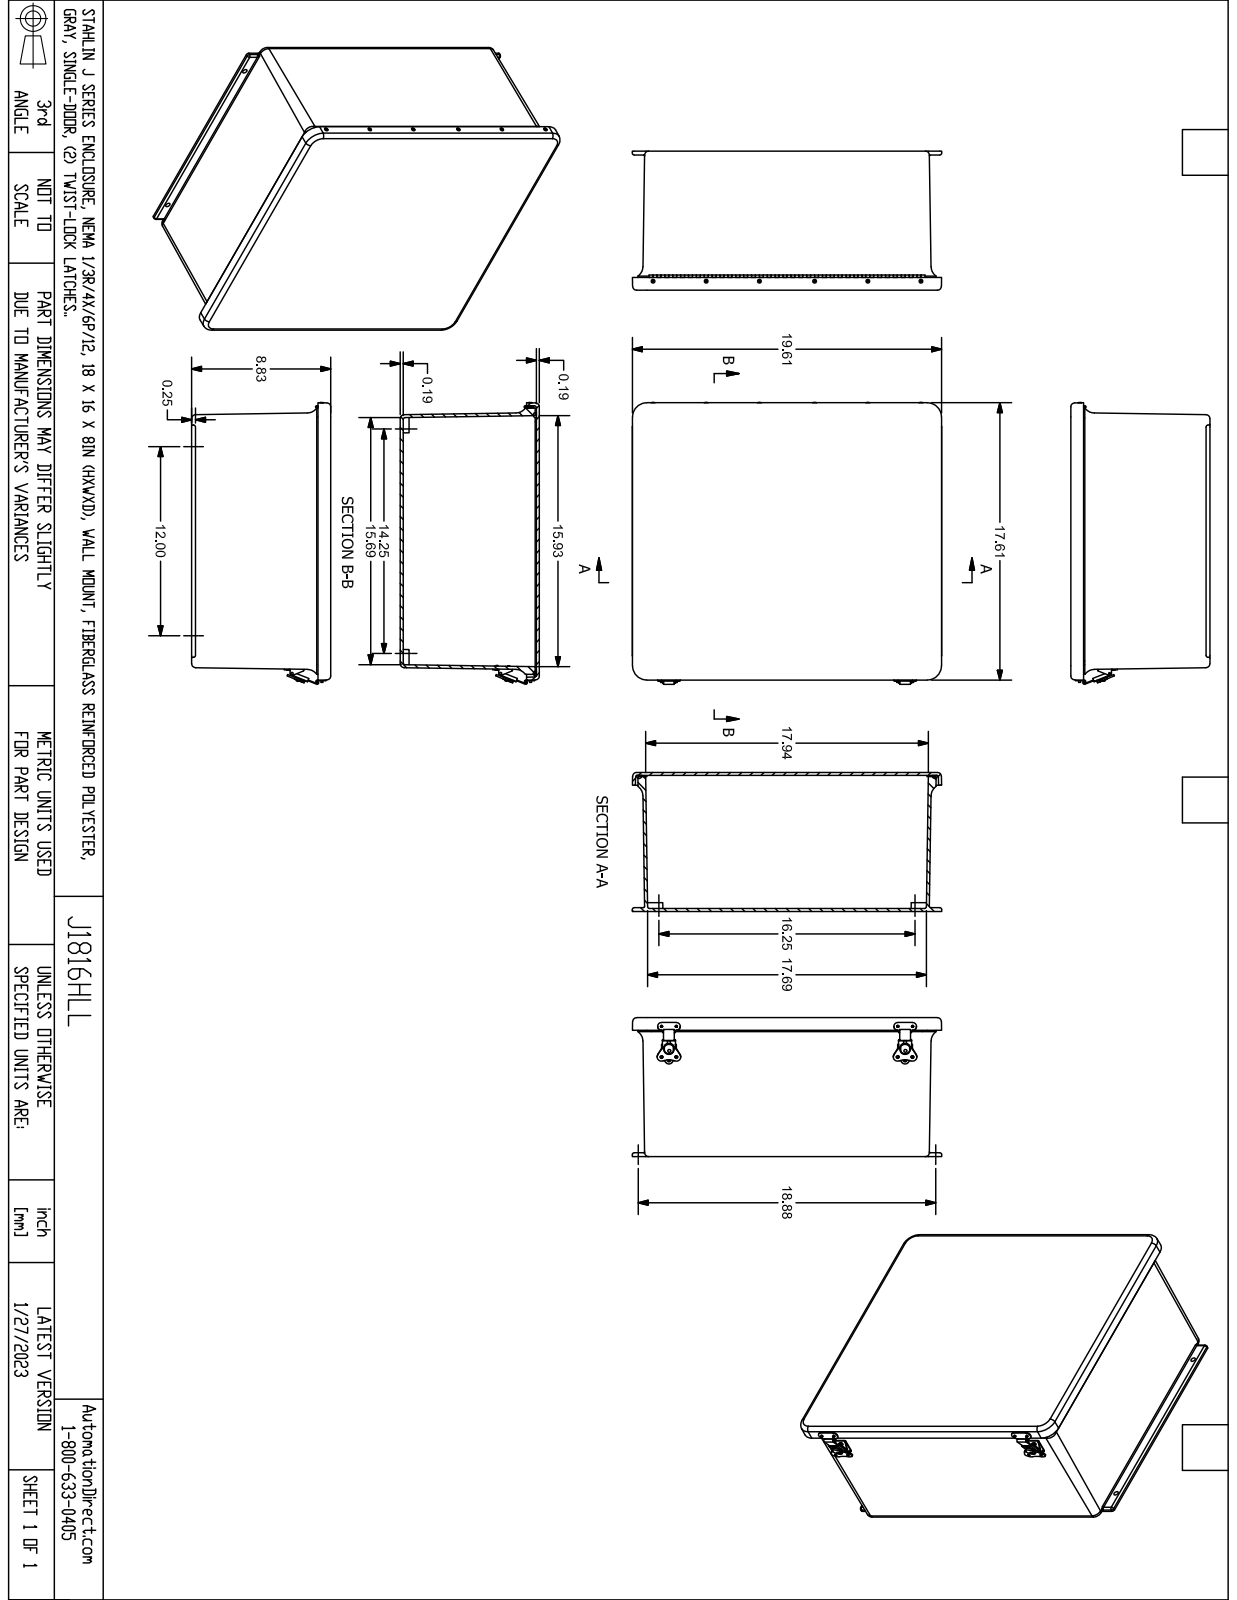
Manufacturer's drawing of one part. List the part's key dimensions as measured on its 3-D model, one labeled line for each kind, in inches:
Part name (STEP PRODUCT): M1816HLL
STEP written by: SolidWorks 2018 (AUTOMOTIVE_DESIGN)
Units: inches
Bodies: 46 solids, 1147 faces (558 planar, 469 cylindrical, 120 other)
Overall size (bounding box): 19.63 × 17.894 × 8.826
Volume: 260.6 in³ · Surface area: 2 733 in²
Round holes (diameter × count): ⌀0.14 ×22, ⌀0.104 ×20, ⌀0.131 ×12, ⌀0.152 ×8, ⌀0.13 ×4, ⌀0.133 ×4, ⌀0.187 ×4, ⌀0.218 ×4, ⌀0.312 ×4, ⌀0.135 ×2, ⌀0.189 ×2, ⌀0.191 ×2
Round bosses / shafts (diameter × count): ⌀0.125 ×15, ⌀0.125 ×7, ⌀0.66 ×2, ⌀0.582 ×2, ⌀0.525 ×2, ⌀0.286 ×2, ⌀0.213 ×2, ⌀0.18 ×2
Partial cylindrical surfaces — rounded edges, fillets, slot ends (radius × count): R0.125 ×17, R0.015 ×16, R0.06 ×13, R0.25 ×10, R0.011 ×8, R0.02 ×8, R0.055 ×8, R0.07 ×8
Main face-to-face distances: 0.187, 8.826, 8.638, 0.188, 8.638, 8.45, 0.49, 0.302, 0.263, 0.076
Hole centre spacings: 14.984, 3.375, 3.375, 6.75, 14.985, 0.157, 10.25, 0.25
